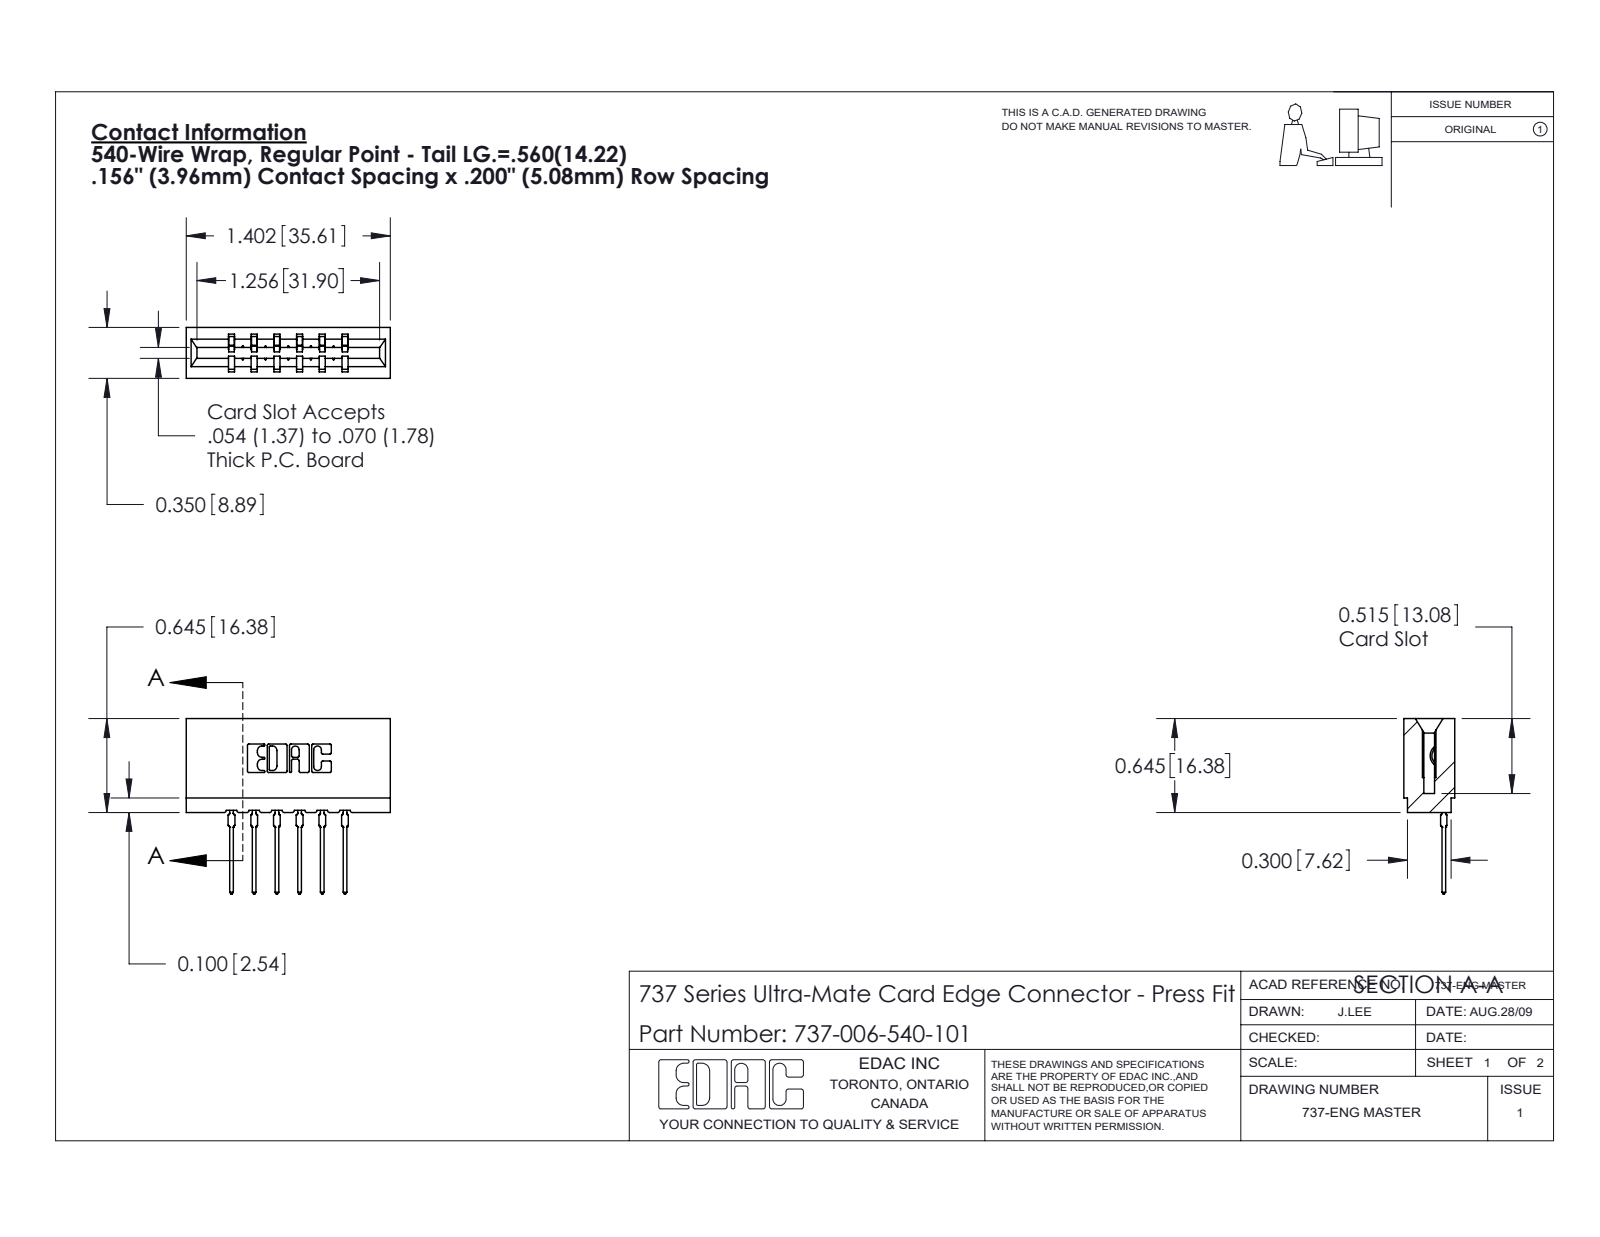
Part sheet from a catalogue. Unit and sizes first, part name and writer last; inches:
Units: inches
Overall size (bounding box): 1.402 × 1.206 × 0.35
Partial cylindrical surfaces — rounded edges, fillets, slot ends (radius × count): R0.01 ×22, R0.015 ×12, R0.021 ×12, R0.007 ×6, R0.031 ×6, R0.005 ×4, R0.011 ×4, R0.026 ×3
Main face-to-face distances: 0.156, 0.138, 0.212, 0.35, 0.312, 0.354, 0.198, 0.074, 0.468, 0.27
Volume: 0.226 in³ · Surface area: 6.798 in²
Bodies: 7 solids, 772 faces (462 planar, 154 cylindrical, 156 other)
Part name (STEP PRODUCT): 745-292-001_540; 737 Part_Insulator Option - 01; 737-006-540-101
STEP written by: SolidWorks 2020 (CONFIG_CONTROL_DESIGN)
